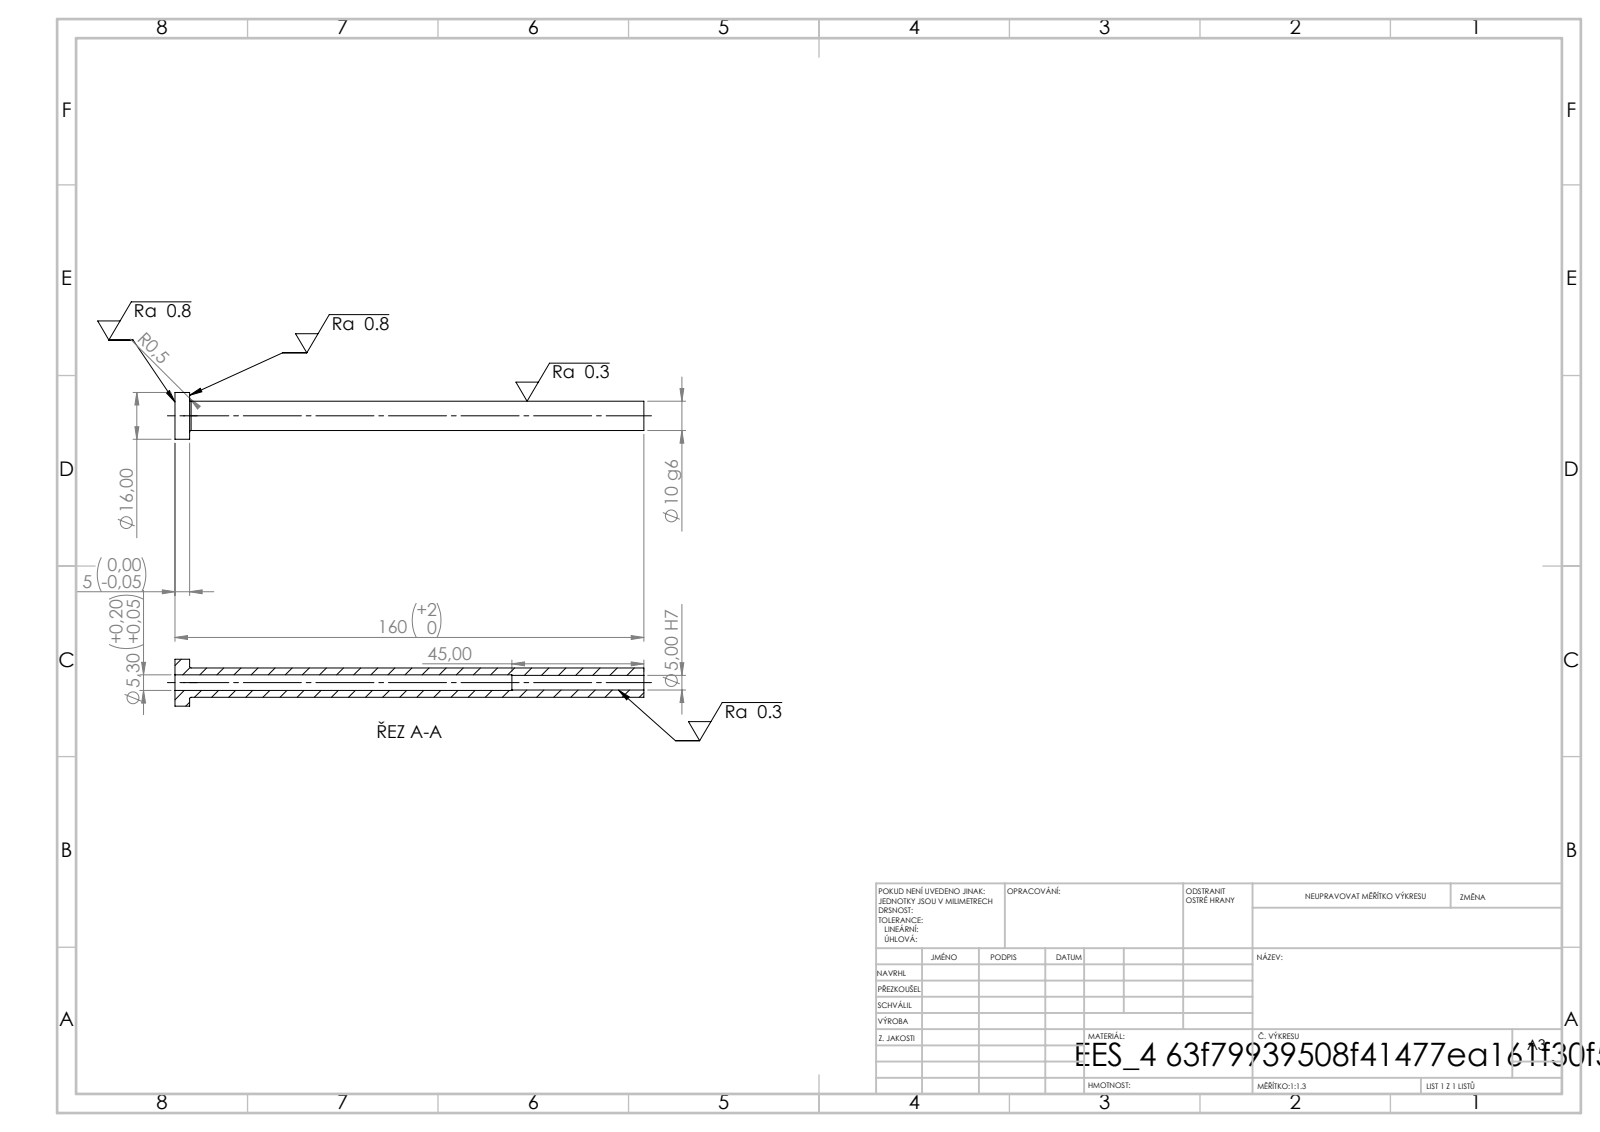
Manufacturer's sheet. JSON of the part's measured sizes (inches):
{"step_written_by": "SolidWorks 2019 (CONFIG_CONTROL_DESIGN)", "units": "inches", "bodies": {"solids": 1, "faces": 14, "planar": 4, "cylindrical": 8, "other": 2}, "overall_size": [6.299, 0.63, 0.63], "volume_in3": 0.596, "surface_area_in2": 12.55, "round_holes": [[0.197, 1], [0.209, 1]], "round_bosses_or_shafts": [[0.63, 1], [0.394, 1]], "face_to_face_distances": [0.197, 6.299, 6.102, 4.528, 4.331, 1.772]}
